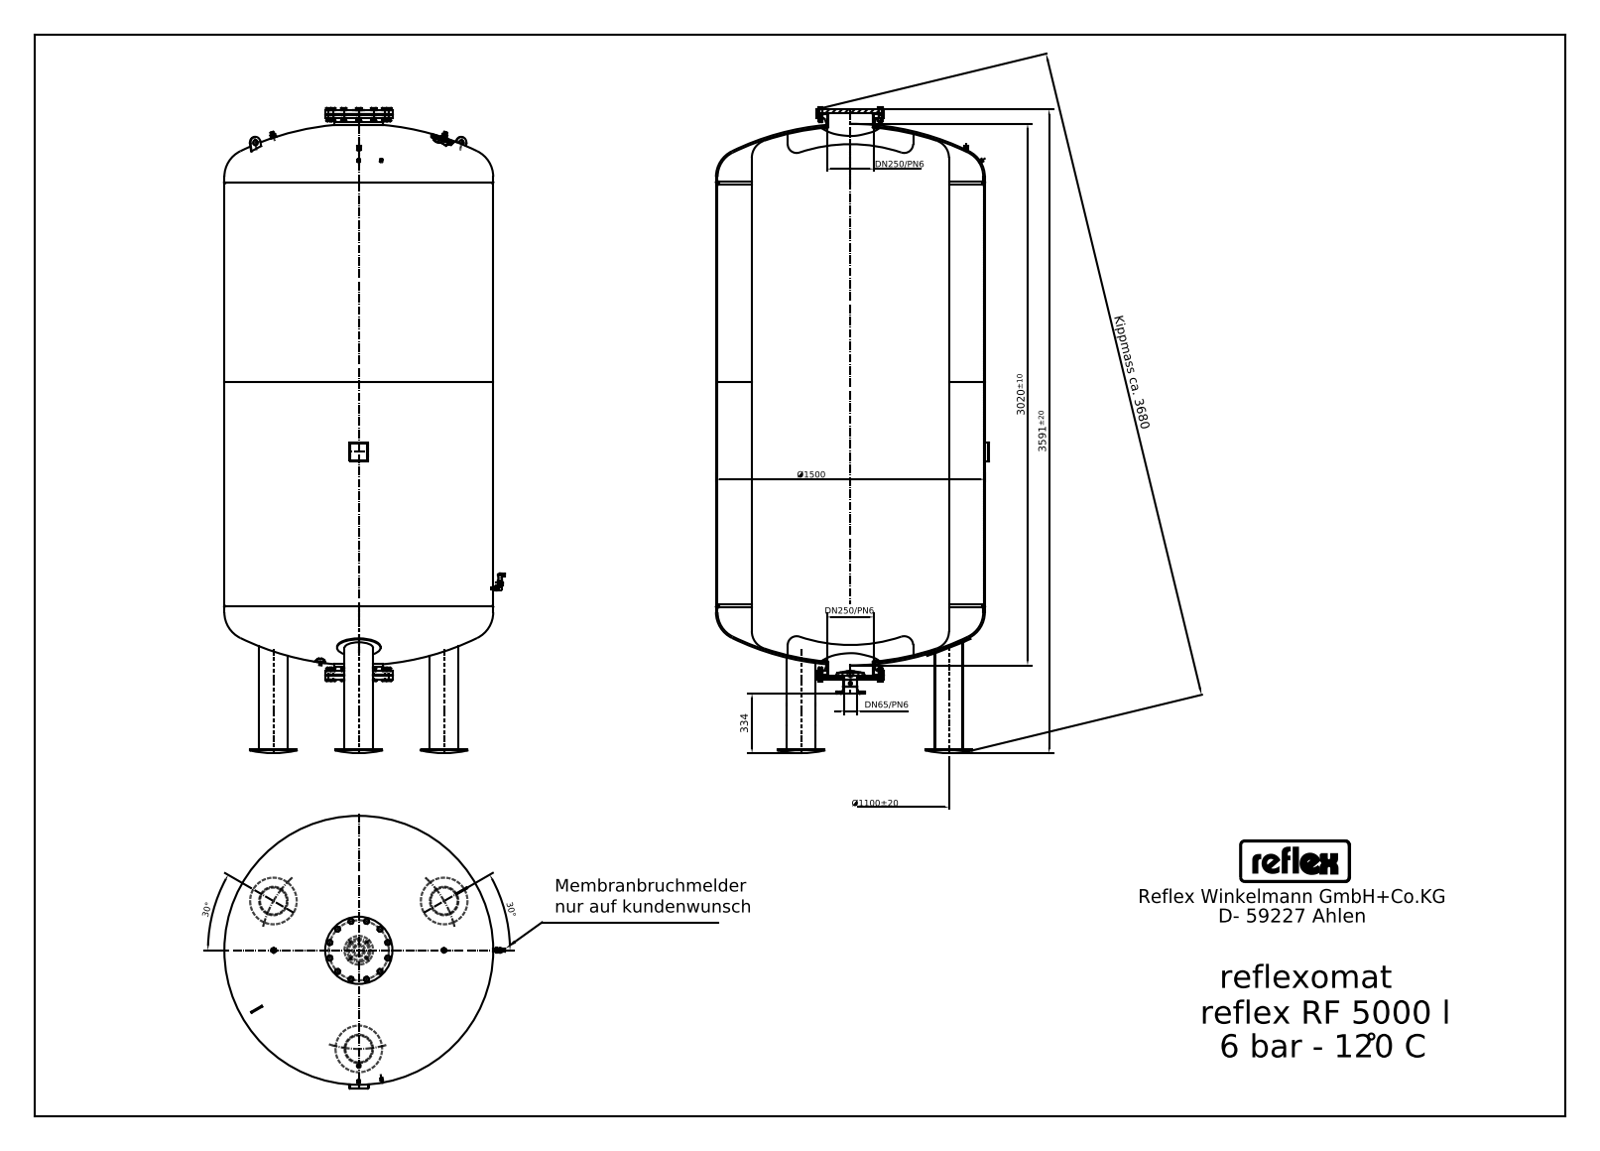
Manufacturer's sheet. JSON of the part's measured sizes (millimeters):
{"step_written_by": "Mechanical Desktop 2009 (CONFIG_CONTROL_DESIGN)", "units": "millimeters", "bodies": {"solids": 23, "faces": 889, "planar": 514, "cylindrical": 207, "other": 168}, "overall_size": [3600, 1566, 1520], "volume_mm3": 5023000000, "surface_area_mm2": 25540000, "round_holes": [[11.45, 2], [3.5, 1], [14.95, 1], [30, 1], [260.4, 1]], "round_bosses_or_shafts": [[16, 12], [159, 3], [21.3, 3], [18.5, 3], [28, 2], [20, 2], [1500, 1], [375, 1]], "partial_cylinders_radius": [[1, 5], [8.44, 4], [3.38, 3], [6, 3], [2, 2], [3, 2], [5.76, 2], [10.12, 2]], "face_to_face_distances": [2360, 22, 3155, 27, 3128, 384, 2749, 389, 2771, 411], "hole_center_spacings": [645, 769.5, 1004.07]}
